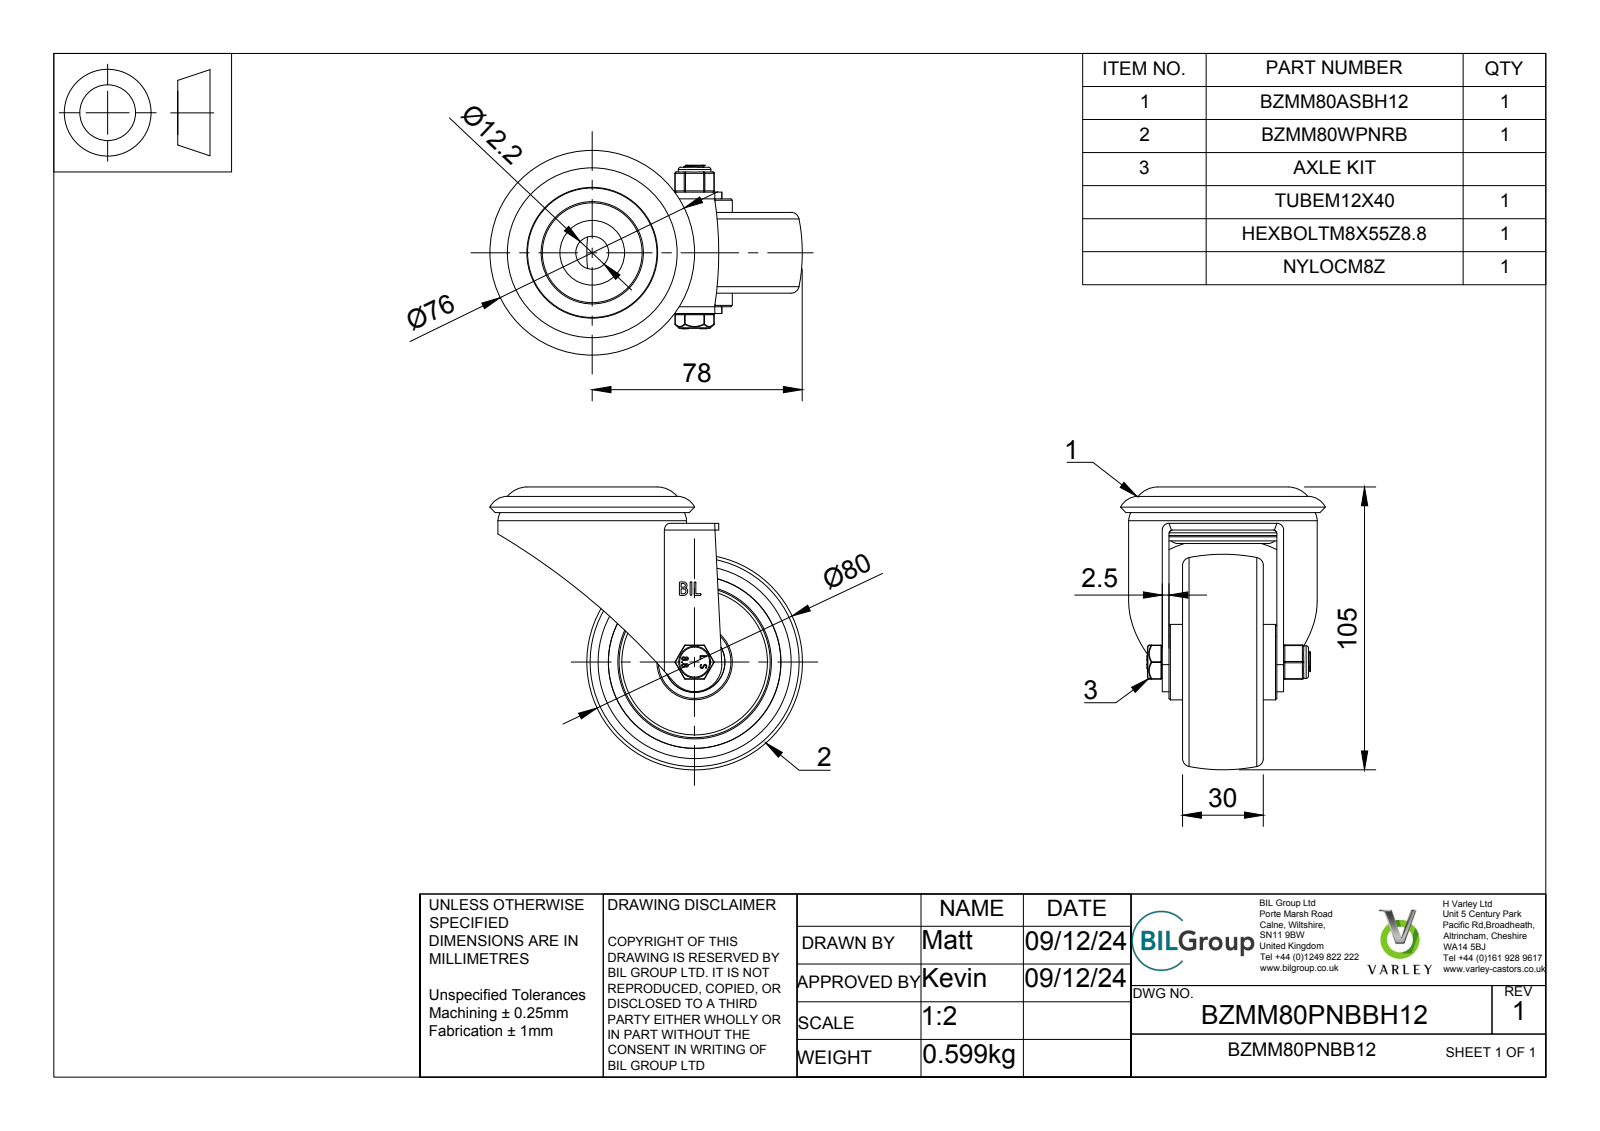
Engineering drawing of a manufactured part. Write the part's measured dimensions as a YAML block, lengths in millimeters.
part_name: "BZMM80PNBBH12 v3; BZMM80ASBH12 v1; ZINC PLATED, PRESSED STEEL FORKS; ZINC PLATED, PRESSED STEEL TOP PLATE (+7 more)"
step_written_by: "Autodesk Translation Framework v13.20.0.188 (AP242_MANAGED_MODEL_BASED_3D_ENGINEERING_MIM_LF)"
units: millimeters
bodies: {solids: 16, faces: 420, planar: 165, cylindrical: 152, other: 103}
overall_size: [116, 105, 76]
volume: 156556
surface_area: 92603
round_holes:
  - {diameter: 0.66, count: 2}
  - {diameter: 8, count: 1}
  - {diameter: 8.2, count: 1}
  - {diameter: 8.4, count: 1}
  - {diameter: 8.6, count: 1}
  - {diameter: 12.2, count: 1}
  - {diameter: 12.5, count: 1}
  - {diameter: 13, count: 1}
  - {diameter: 20, count: 1}
  - {diameter: 64, count: 1}
  - {diameter: 65, count: 1}
  - {diameter: 72, count: 1}
round_bosses_or_shafts:
  - {diameter: 5.5, count: 6}
  - {diameter: 70, count: 1}
  - {diameter: 49.5, count: 1}
  - {diameter: 38, count: 1}
  - {diameter: 28, count: 1}
  - {diameter: 24, count: 1}
  - {diameter: 22.5, count: 1}
  - {diameter: 21.31, count: 1}
partial_cylinders:
  - {radius: 0.5, count: 18}
  - {radius: 0.25, count: 12}
  - {radius: 0.33, count: 4}
  - {radius: 0.64, count: 4}
  - {radius: 1.25, count: 4}
  - {radius: 0.63, count: 2}
  - {radius: 0.64, count: 2}
  - {radius: 2.5, count: 2}
face_to_face_distances: [13, 17, 5, 18, 35, 22, 2.5, 42.5, 7.5, 20.5]
hole_center_spacings: [3.22, 2.49]
